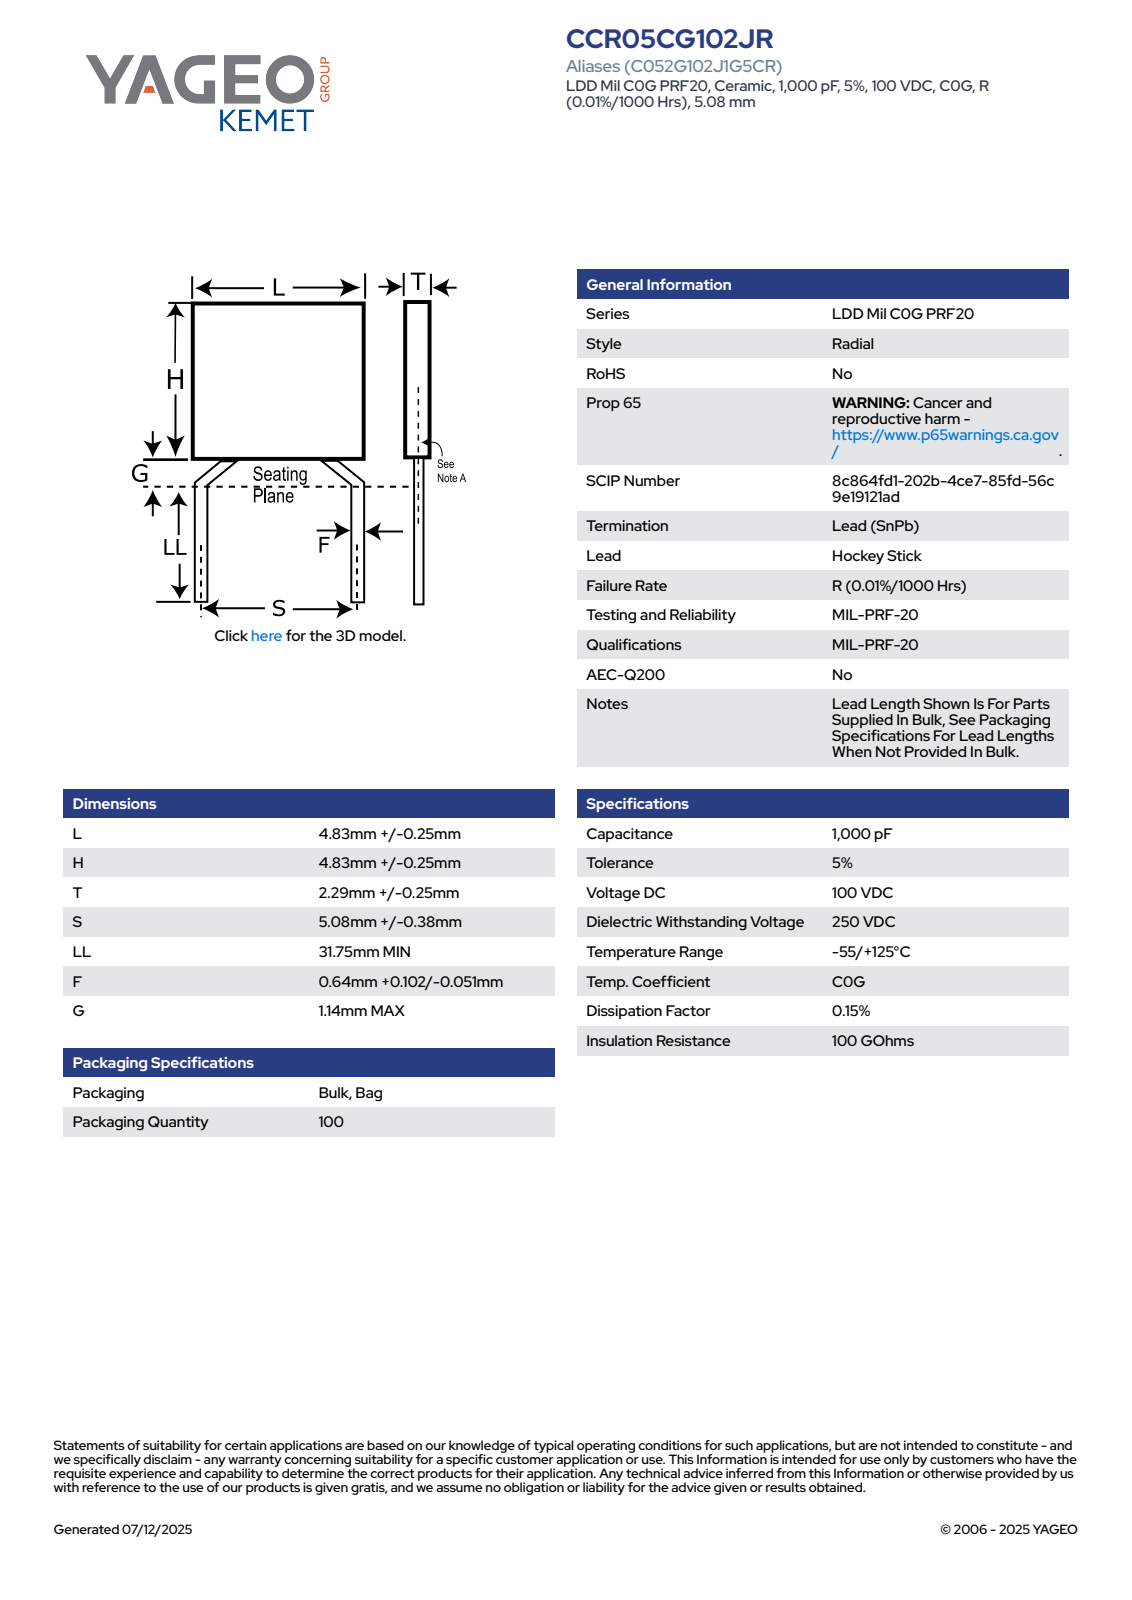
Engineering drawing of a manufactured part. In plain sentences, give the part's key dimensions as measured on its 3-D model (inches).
The part is named "CCRM_HS_C052_L5.08H5.08T2.54S5.08LL31.75F0.742G1.14K". Its 3-D file was written by "SolidWorks 2014 (AUTOMOTIVE_DESIGN)". It is 4 solids with 73 faces: 65 planar, 4 cylindrical and 4 other. Overall it measures 1.495 by 0.229 by 0.1 inches. Its volume is 0.006 cubic inches and its surface area 0.408 square inches. Round bosses or shafts: 2 of diameter 0.029. The main face-to-face distances are 0.1, 0.2, 1.295, 1.495, 0.036, 1.417, 0.122, 0.078, 1.381, 0.087.
